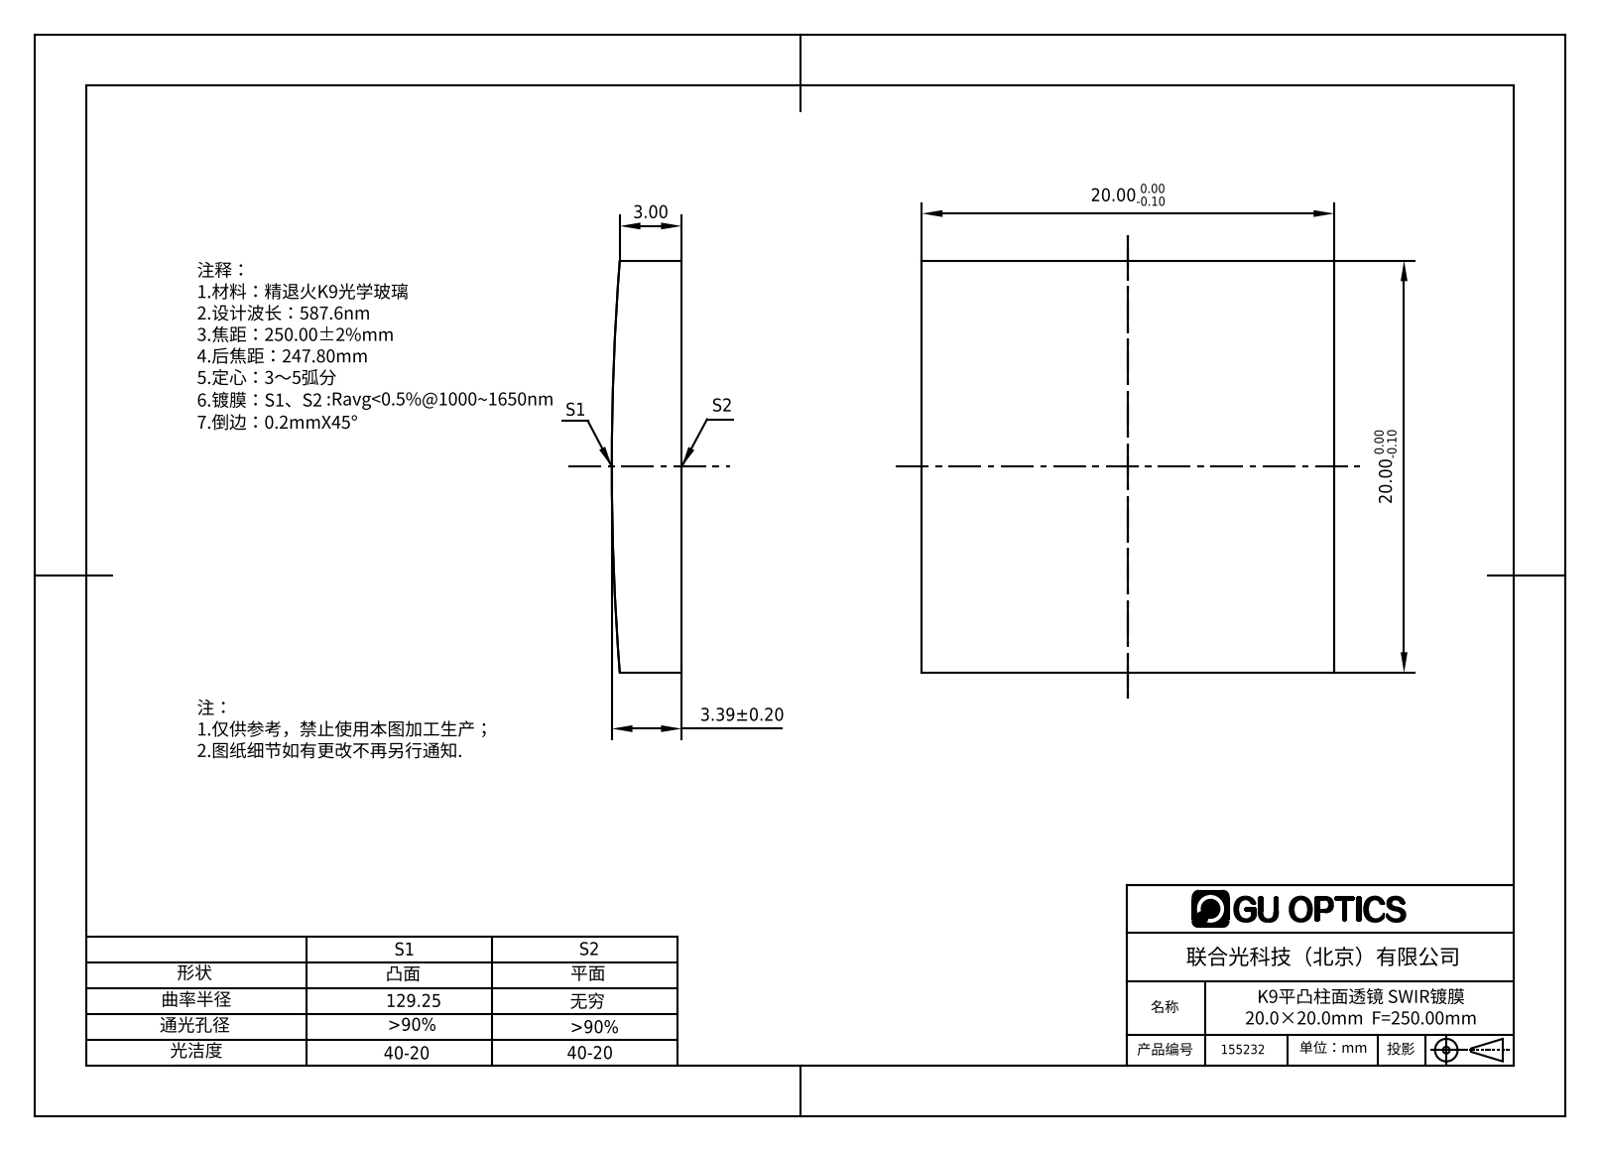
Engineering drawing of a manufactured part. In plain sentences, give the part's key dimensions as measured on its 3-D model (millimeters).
The part is named "155034". Its 3-D file was written by "SolidWorks 2016 (AUTOMOTIVE_DESIGN)". It is 1 solid with 6 faces: 5 planar, 1 cylindrical and 0 other. Overall it measures 20 by 20 by 3.39 millimeters. Its volume is 1 304 cubic millimeters and its surface area 1 051 square millimeters. Partial cylindrical surfaces (rounded edges, fillets, slot ends): 1 of radius 129.25. The main face-to-face distances are 20.
